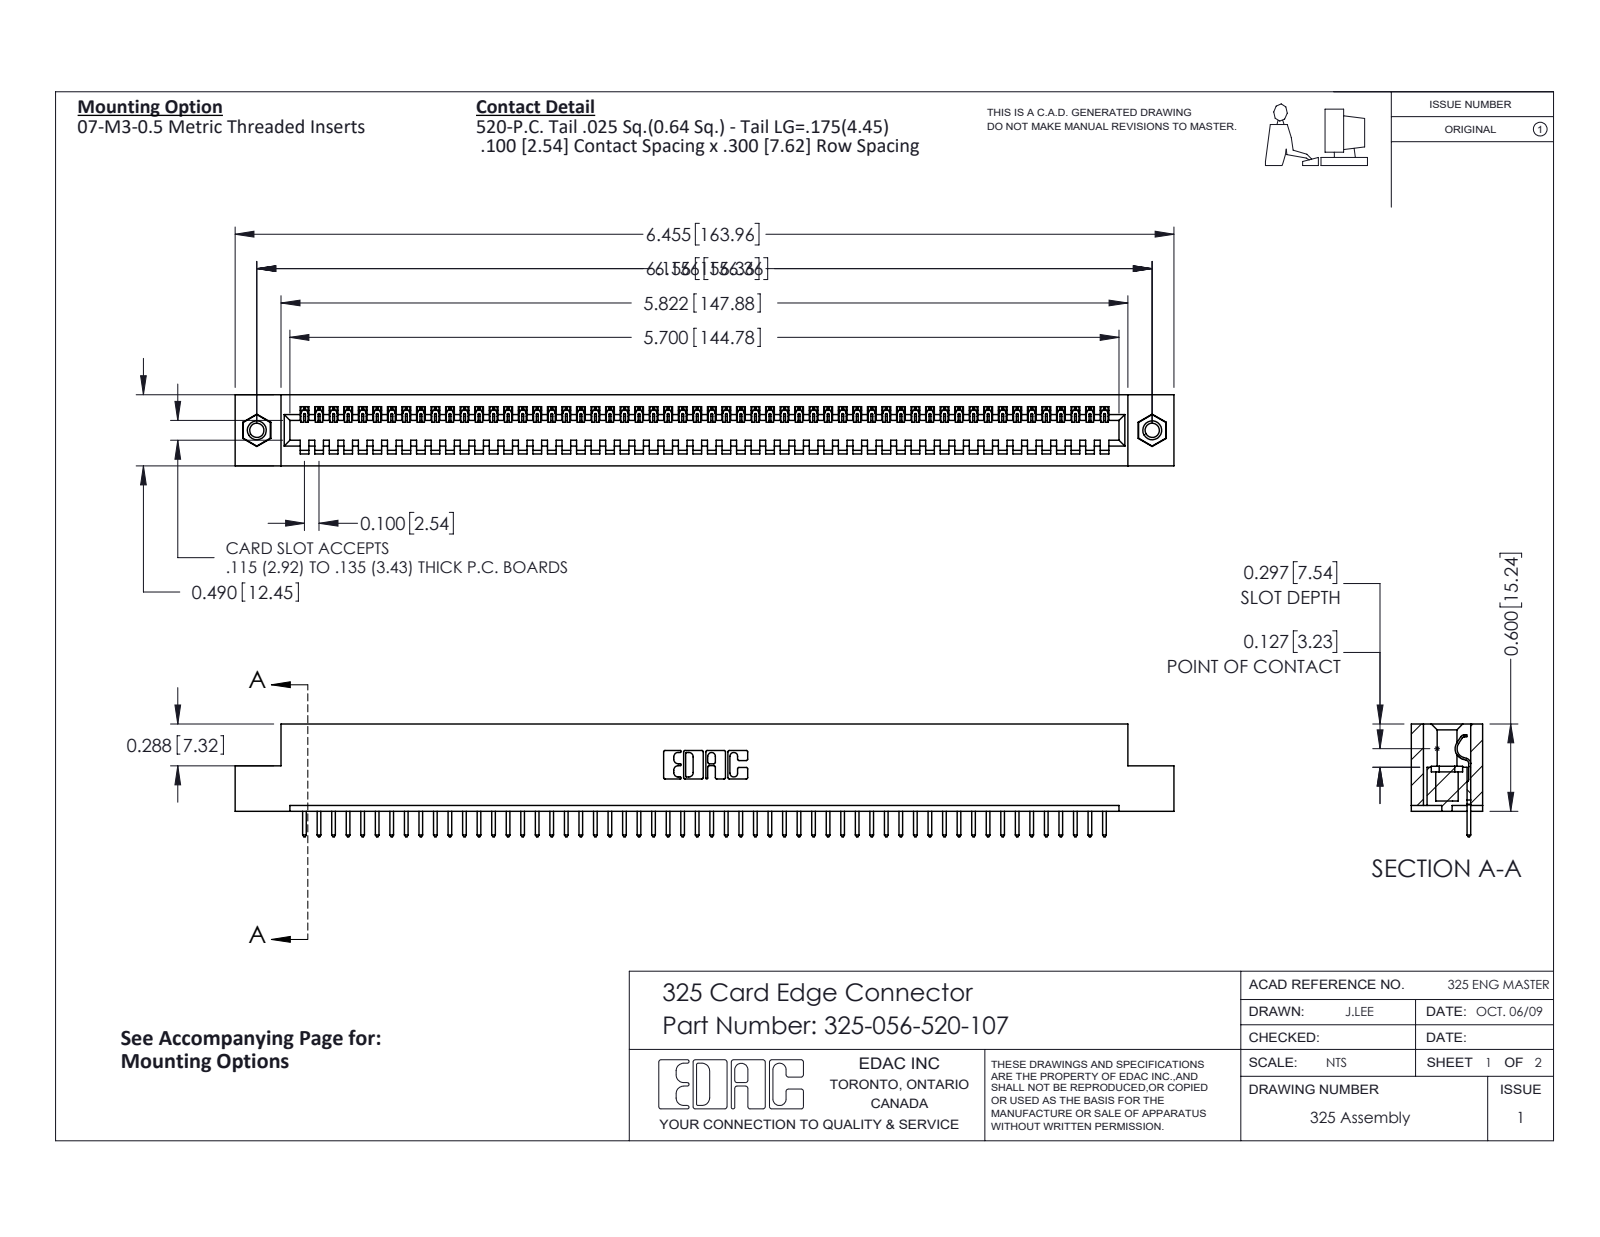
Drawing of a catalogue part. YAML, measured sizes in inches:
part_name: "325 Part_TI; 325-056-520-107; 345-250-001_345-250-005-103; 325-292-001_325-293-120"
step_written_by: "SolidWorks 2016 (CONFIG_CONTROL_DESIGN)"
units: inches
bodies: {solids: 59, faces: 3422, planar: 2454, cylindrical: 952, other: 16}
overall_size: [6.455, 0.775, 0.49]
volume: 1.267
surface_area: 34.66
round_holes:
  - {diameter: 0.098, count: 2}
  - {diameter: 0.125, count: 2}
  - {diameter: 0.16, count: 2}
round_bosses_or_shafts:
  - {diameter: 0.155, count: 2}
partial_cylinders:
  - {radius: 0.006, count: 112}
  - {radius: 0.01, count: 112}
  - {radius: 0.01, count: 22}
  - {radius: 0.007, count: 6}
  - {radius: 0.031, count: 6}
  - {radius: 0.026, count: 3}
  - {radius: 0.014, count: 1}
  - {radius: 0.022, count: 1}
face_to_face_distances: [0.083, 0.407, 0.49, 0.3, 0.107, 0.383, 0.025, 0.325, 0.263, 0.56]
hole_center_spacings: [6.156]
